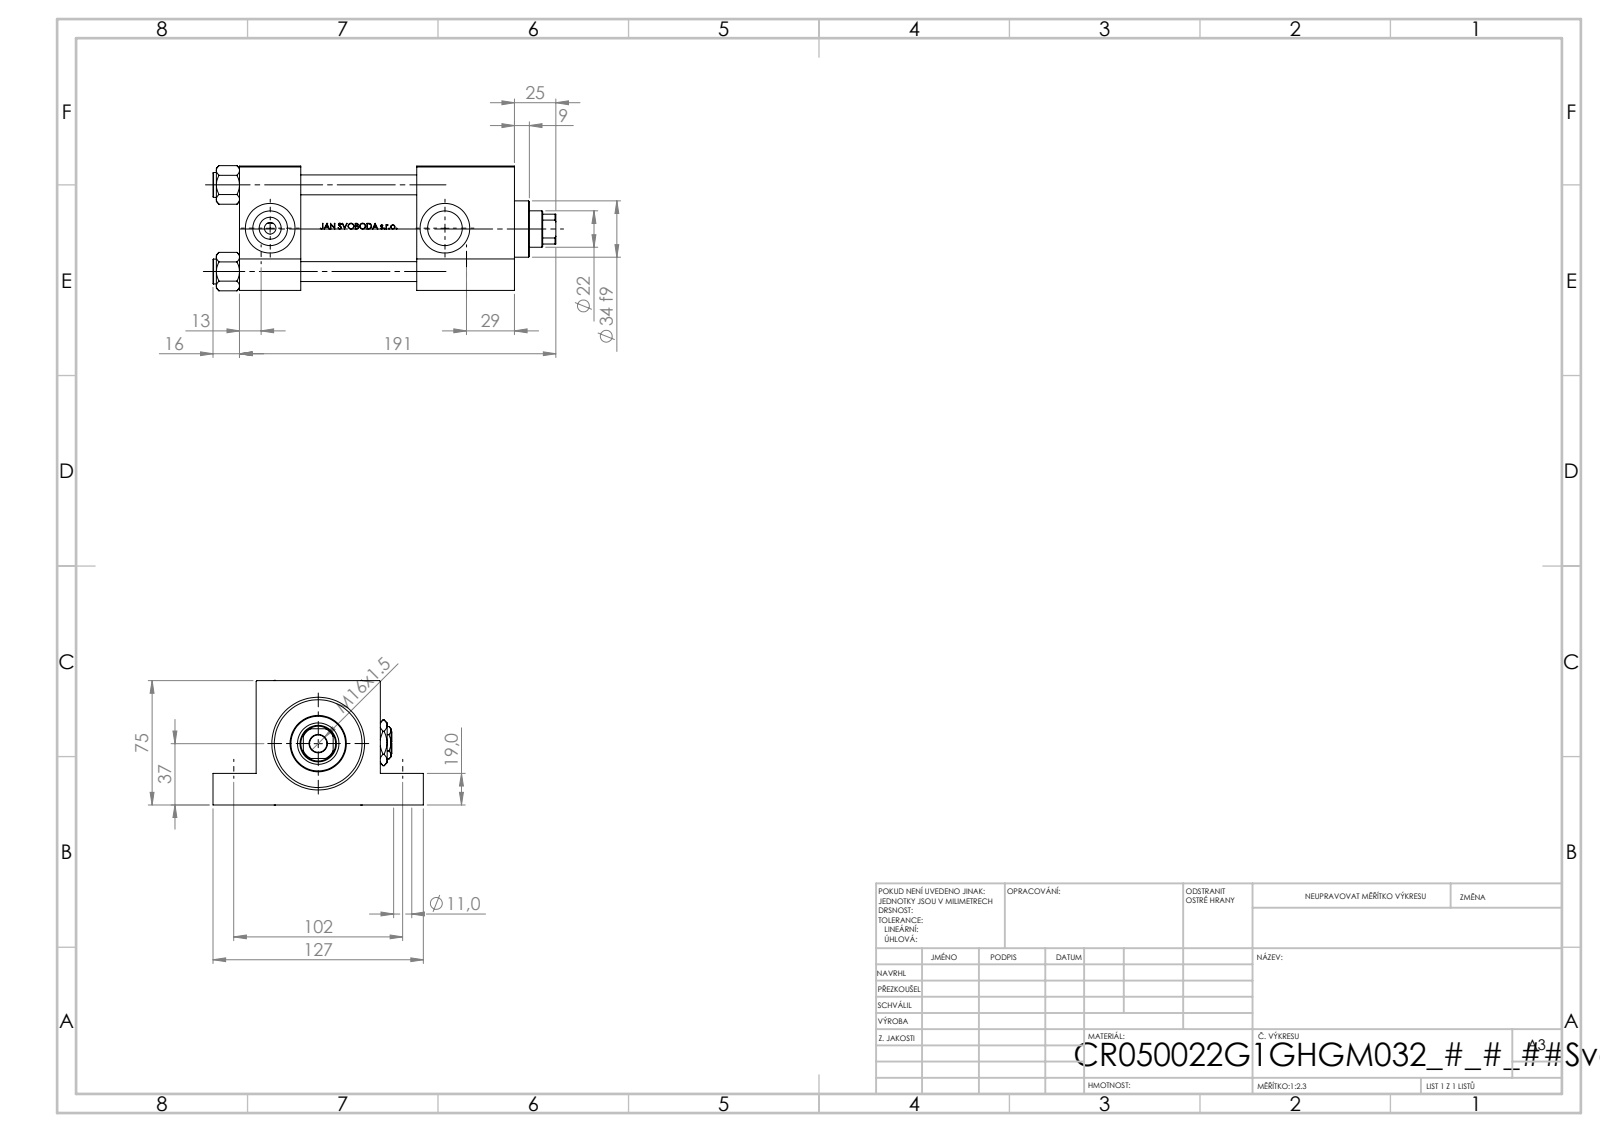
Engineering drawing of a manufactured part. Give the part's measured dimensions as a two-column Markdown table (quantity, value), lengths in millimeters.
| quantity | value |
| --- | --- |
| part name | V215CR_VCP_G; V215CR_G_TYCINKA; V215_VC_A; V215CR_G_Body (+2 more) |
| STEP written by | SolidWorks 2019 (CONFIG_CONTROL_DESIGN) |
| units | millimeters |
| bodies | 12 solids, 1134 faces (454 planar, 128 cylindrical, 552 other) |
| overall size | 207 × 127 × 75.54 |
| volume | 768 388 mm³ |
| surface area | 167 939 mm² |
| round holes (diameter × count) | 11 × 4, 12 × 4, 7 × 2, 20.96 × 2, 30 × 2, 10.5 × 1, 22 × 1, 25 × 1, 41 × 1, 50 × 1, 53 × 1 |
| round bosses / shafts (diameter × count) | 15 × 4, 56 × 1, 34 × 1 |
| partial cylindrical surfaces (radius × count) | 10.5 × 1 |
| main face-to-face distances | 75, 37, 166, 129, 19, 56, 70, 107, 59, 26 |
| hole center spacings | 52.3, 36.63, 37.34, 73.96, 102, 124, 160.56, 105.5 |
